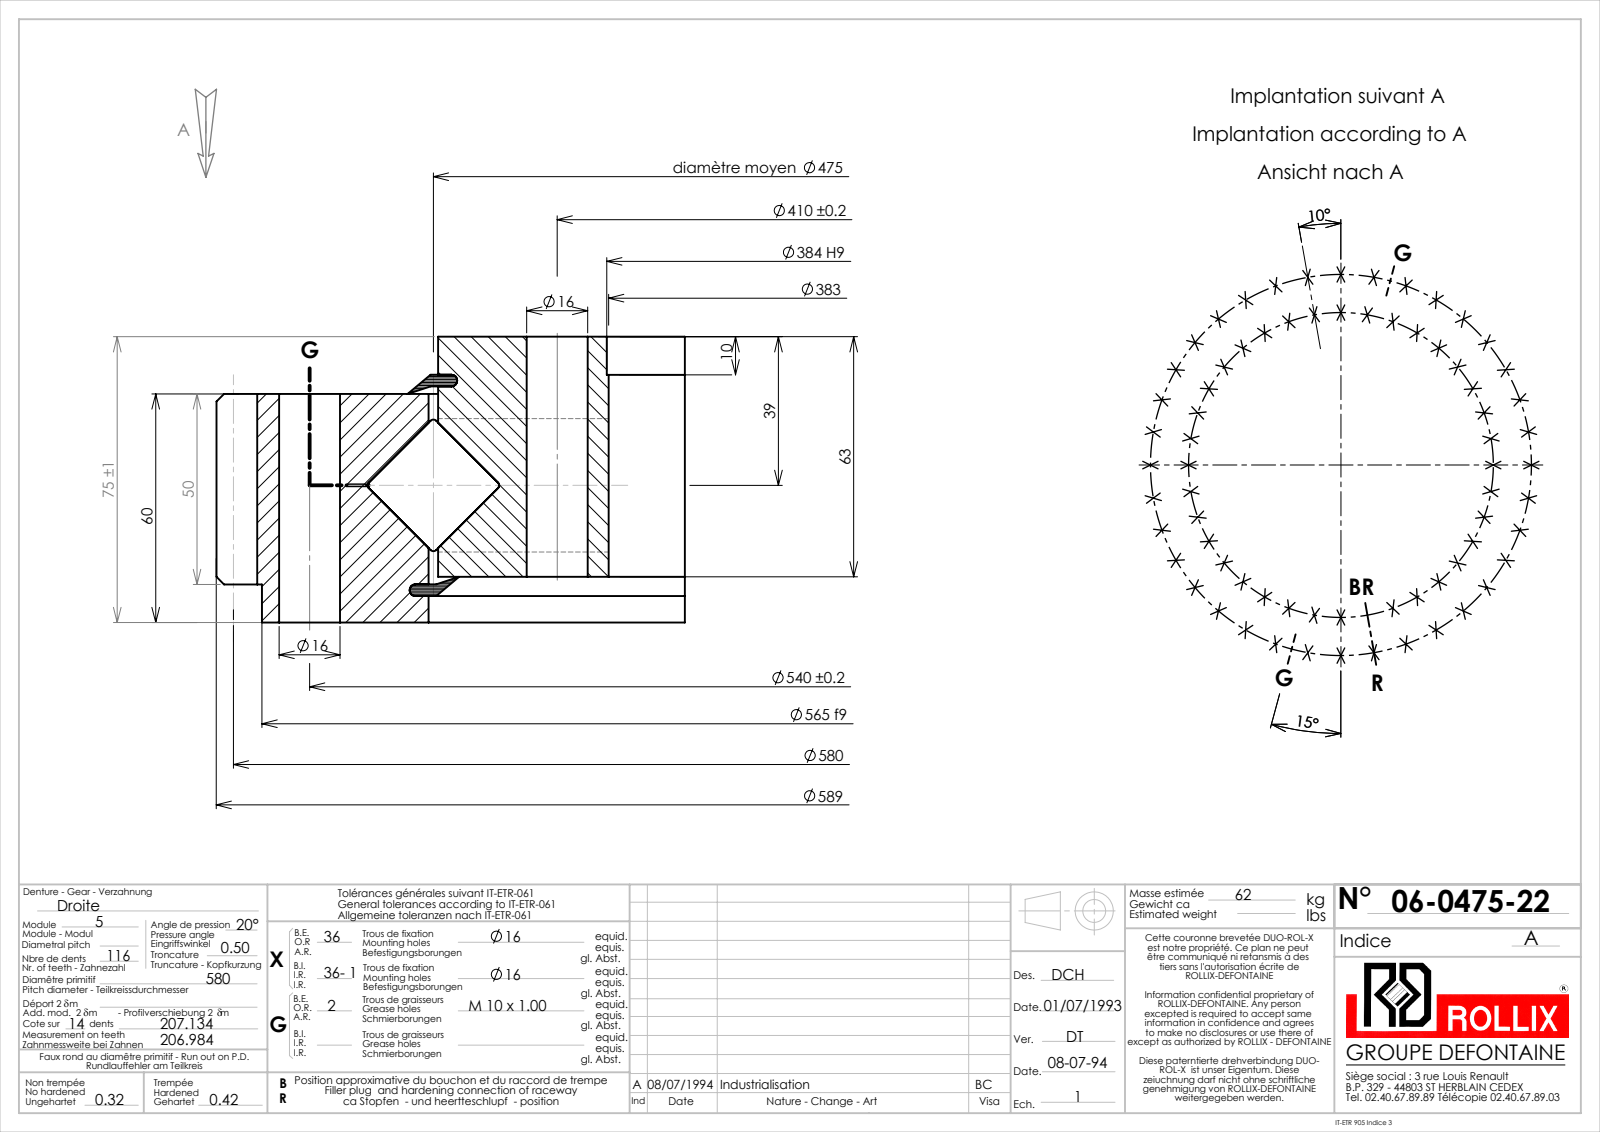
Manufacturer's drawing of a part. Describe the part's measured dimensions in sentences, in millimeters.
The part is named "06-0475-22". Its 3-D file was written by "SolidWorks 2016 (CONFIG_CONTROL_DESIGN)". It is 5 solids with 921 faces: 248 planar, 399 cylindrical and 274 other. Overall it measures 588.89 by 588.89 by 75 millimeters. Its volume is 7 090 000 cubic millimeters and its surface area 1 093 000 square millimeters. Round holes: 71 of diameter 16, 2 of diameter 9, 1 of diameter 383, 1 of diameter 384, 1 of diameter 477.5. Round bosses or shafts: 1 of diameter 565, 1 of diameter 472.5, 1 of diameter 25. Partial cylindrical surfaces (rounded edges, fillets, slot ends): 1 of radius 283.75, 1 of radius 294.5. The main face-to-face distances are 60, 12, 48, 75, 63, 15, 55, 1.95, 49.95, 3.1. The hole center spacings are 270, 521.6, 531.8, 47.06, 93.77, 139.76, 184.69, 381.84.
